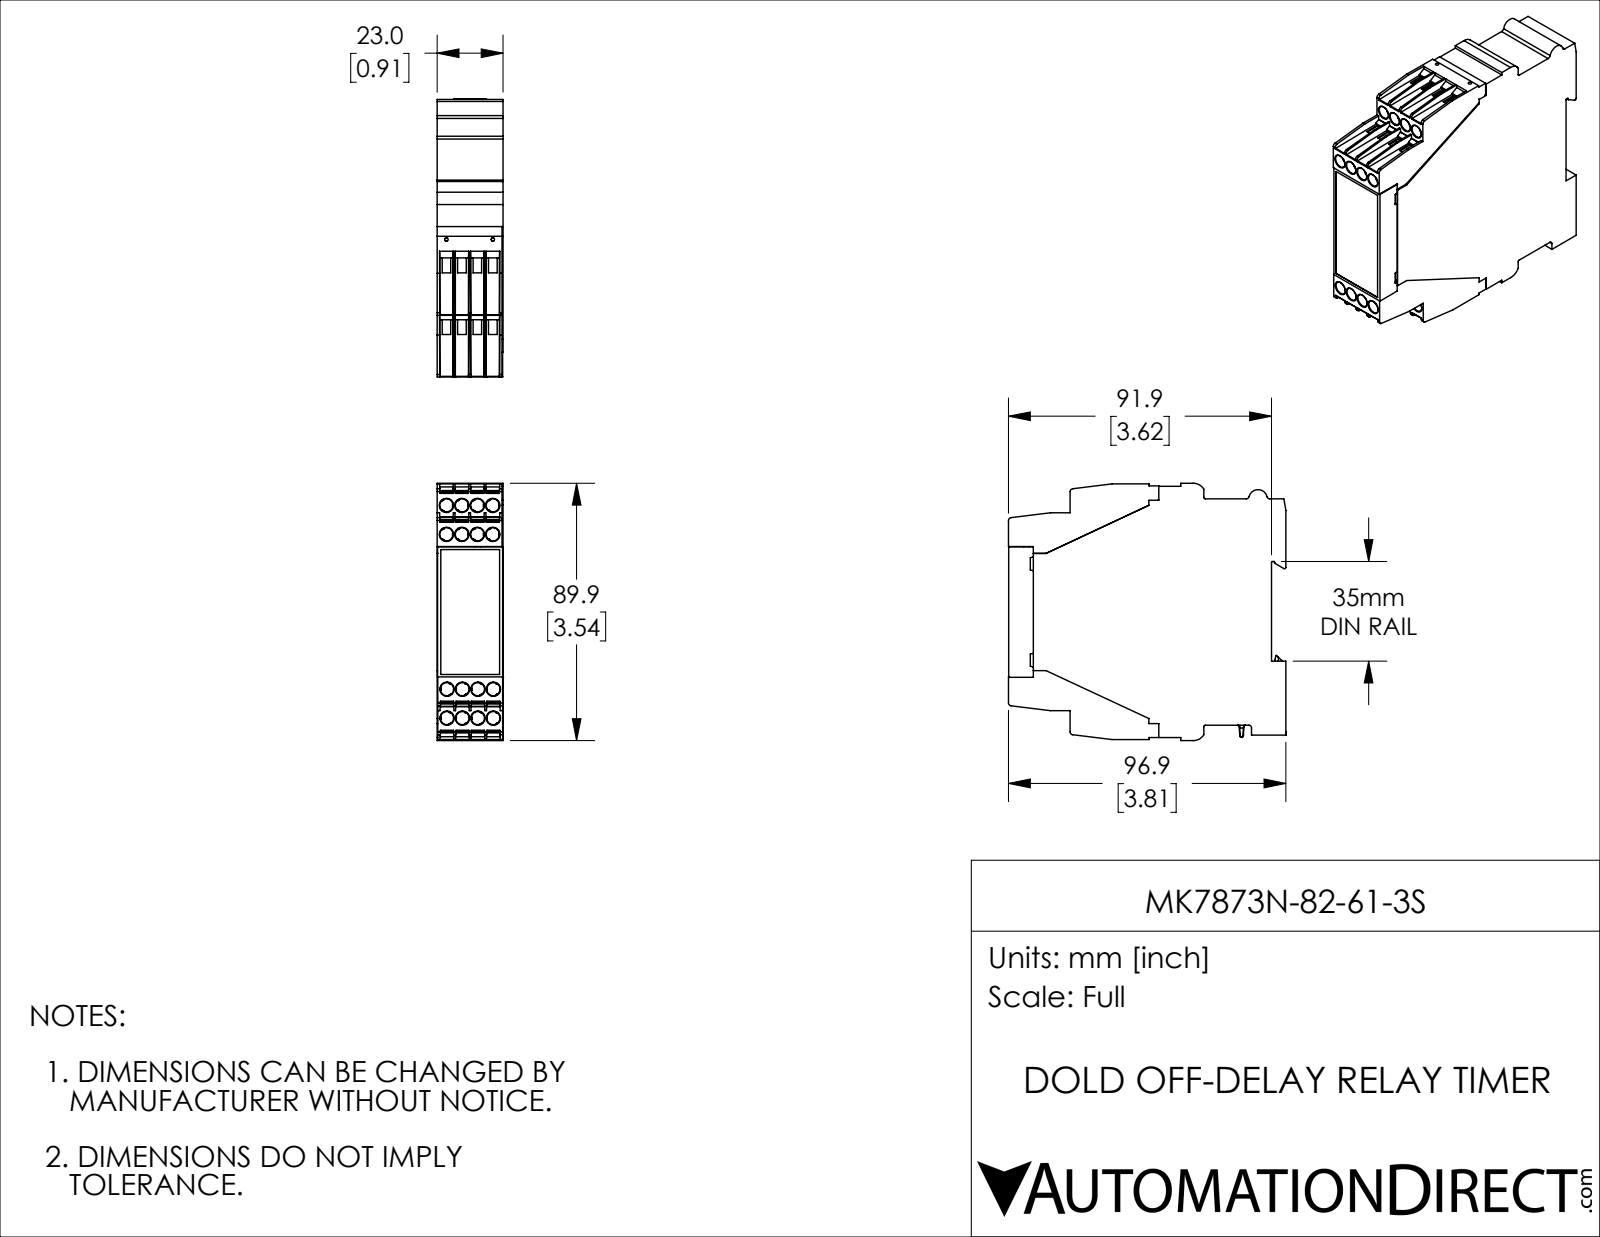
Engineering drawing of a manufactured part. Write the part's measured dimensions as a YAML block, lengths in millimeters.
part_name: "MK7873N-82-61-3S"
step_written_by: "SolidWorks 2019 (CONFIG_CONTROL_DESIGN)"
units: millimeters
bodies: {solids: 4, faces: 698, planar: 556, cylindrical: 99, other: 43}
overall_size: [97.1, 89.8, 23]
volume: 172900
surface_area: 34740
round_holes:
  - {diameter: 4.6, count: 16}
  - {diameter: 1.2, count: 4}
partial_cylinders:
  - {radius: 1, count: 11}
  - {radius: 0.2, count: 7}
  - {radius: 0.5, count: 7}
  - {radius: 1.5, count: 2}
  - {radius: 4.4, count: 2}
  - {radius: 3.2, count: 1}
face_to_face_distances: [23, 22.9, 22.7, 88.2, 96.7, 8.5, 83.3, 5, 91.7, 22.9]
hole_center_spacings: [5.4, 11.5, 10.1, 10.8, 14.8, 64.2, 16.2, 64.4]
